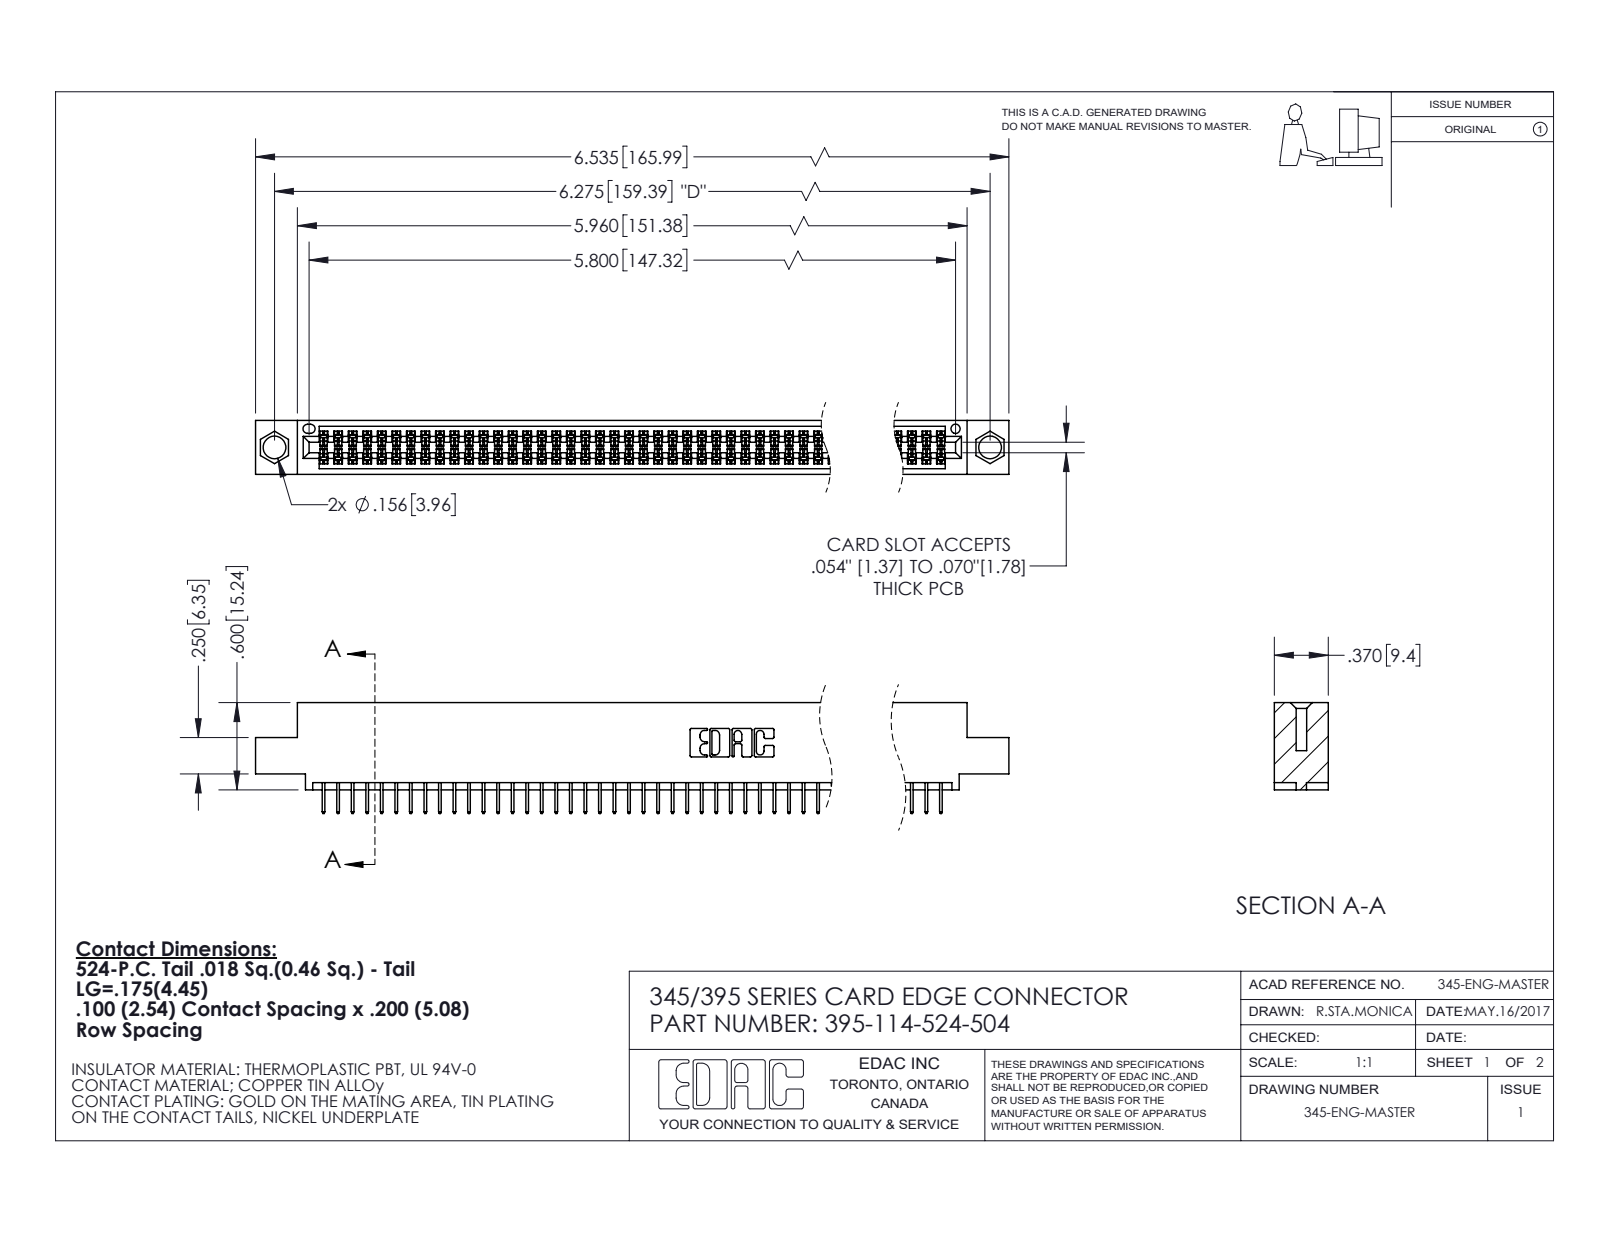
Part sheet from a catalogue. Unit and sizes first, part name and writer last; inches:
Units: inches
Overall size (bounding box): 6.535 × 0.762 × 0.37
Round holes (diameter × count): ⌀0.156 ×2, ⌀0.064 ×1
Partial cylindrical surfaces — rounded edges, fillets, slot ends (radius × count): R0.006 ×228, R0.01 ×22, R0.007 ×6, R0.031 ×6, R0.026 ×3, R0.014 ×2, R0.019 ×2, R0.022 ×2
Main face-to-face distances: 0.072, 0.298, 0.2, 0.37, 0.098, 0.272, 0.025, 0.225, 0.072, 0.175
Hole centre spacings: 0.27, 6.039, 6.275
Volume: 0.971 in³ · Surface area: 36.11 in²
Bodies: 115 solids, 6300 faces (4544 planar, 1756 cylindrical, 0 other)
Part name (STEP PRODUCT): 345 Part_0.110 Offset - 0.156 Dia-TI; 395-114-524-504; 345-292-001_345-293-124
STEP written by: SolidWorks 2020 (CONFIG_CONTROL_DESIGN)
